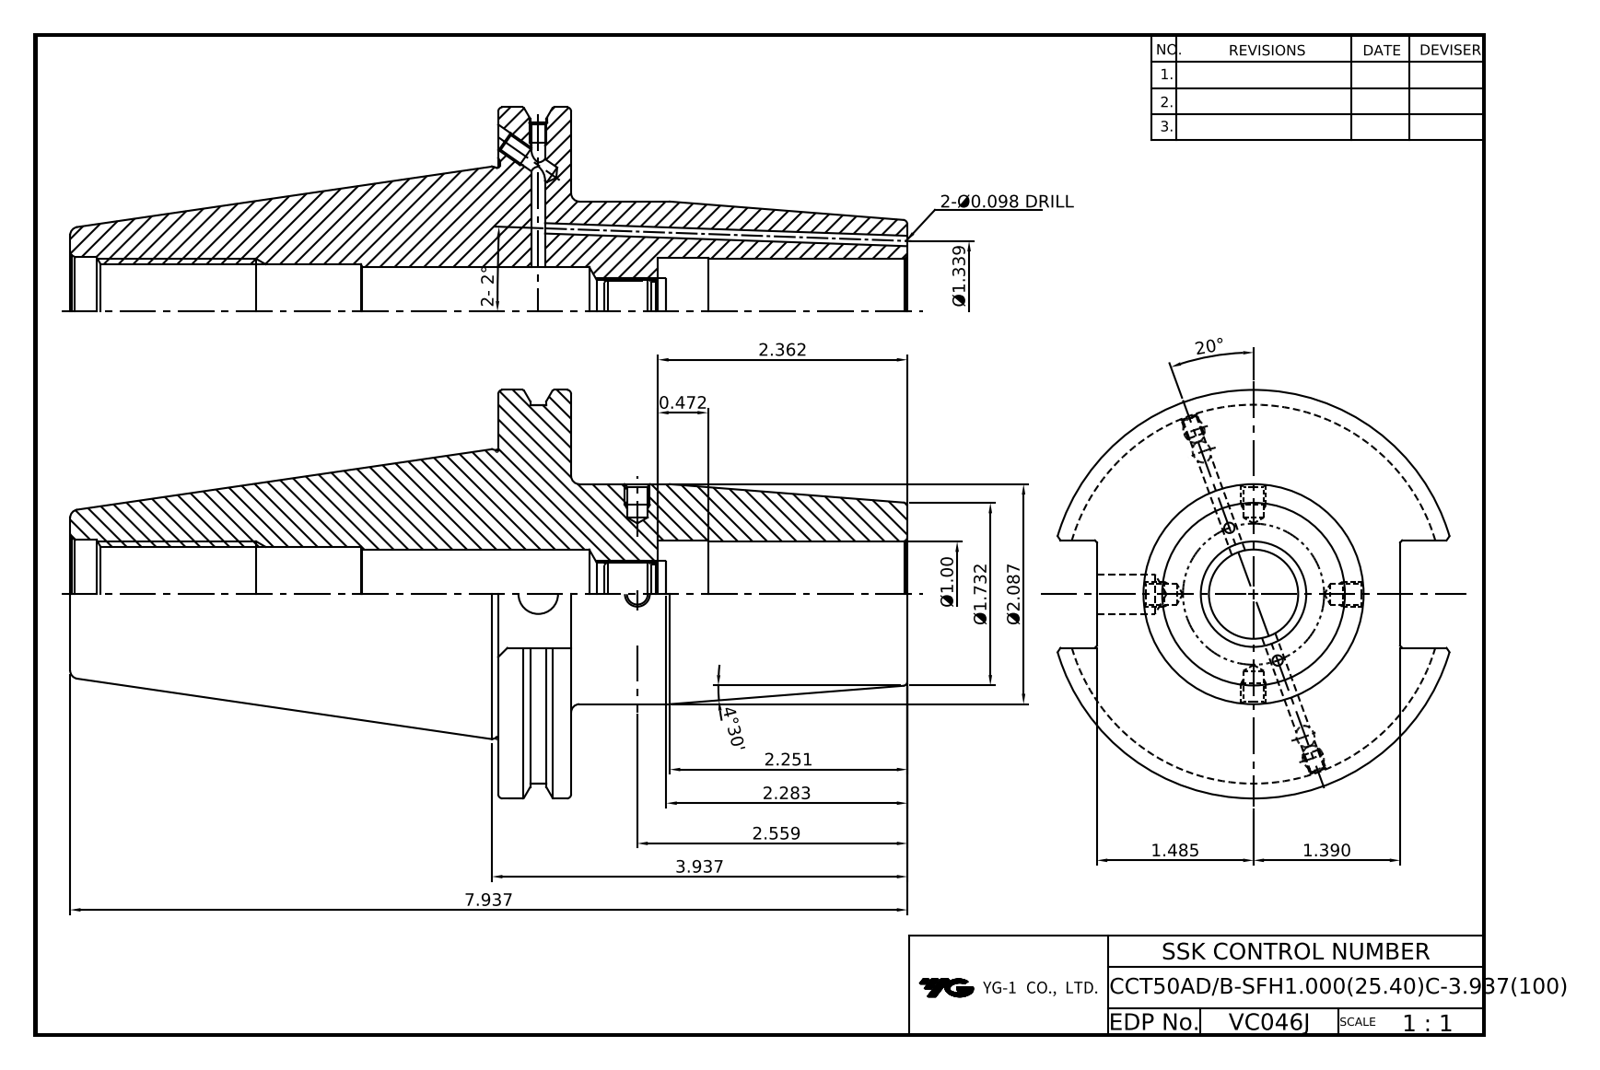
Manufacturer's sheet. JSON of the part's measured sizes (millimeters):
{"part_name": "LO-CCT50ADB-SFH25.4C-3.94", "step_written_by": "Autodesk Inventor 2025 (AUTOMOTIVE_DESIGN)", "units": "millimeters", "bodies": {"solids": 1, "faces": 86, "planar": 38, "cylindrical": 24, "other": 24}, "overall_size": [201.6, 98.42, 94.69], "volume_mm3": 444944, "surface_area_mm2": 63831, "round_holes": [[2.5, 2], [4.13, 2], [4.2, 2], [5, 2], [9.53, 1], [14.92, 1], [21.97, 1], [25.4, 1], [26.2, 1], [26.6, 1]], "round_bosses_or_shafts": [[98.42, 1], [91.29, 1], [69.25, 1], [53, 1]], "face_to_face_distances": [17.55, 98.5, 80.95, 103.1, 120.65, 201.6, 141.6, 38.5, 20.95, 60]}
